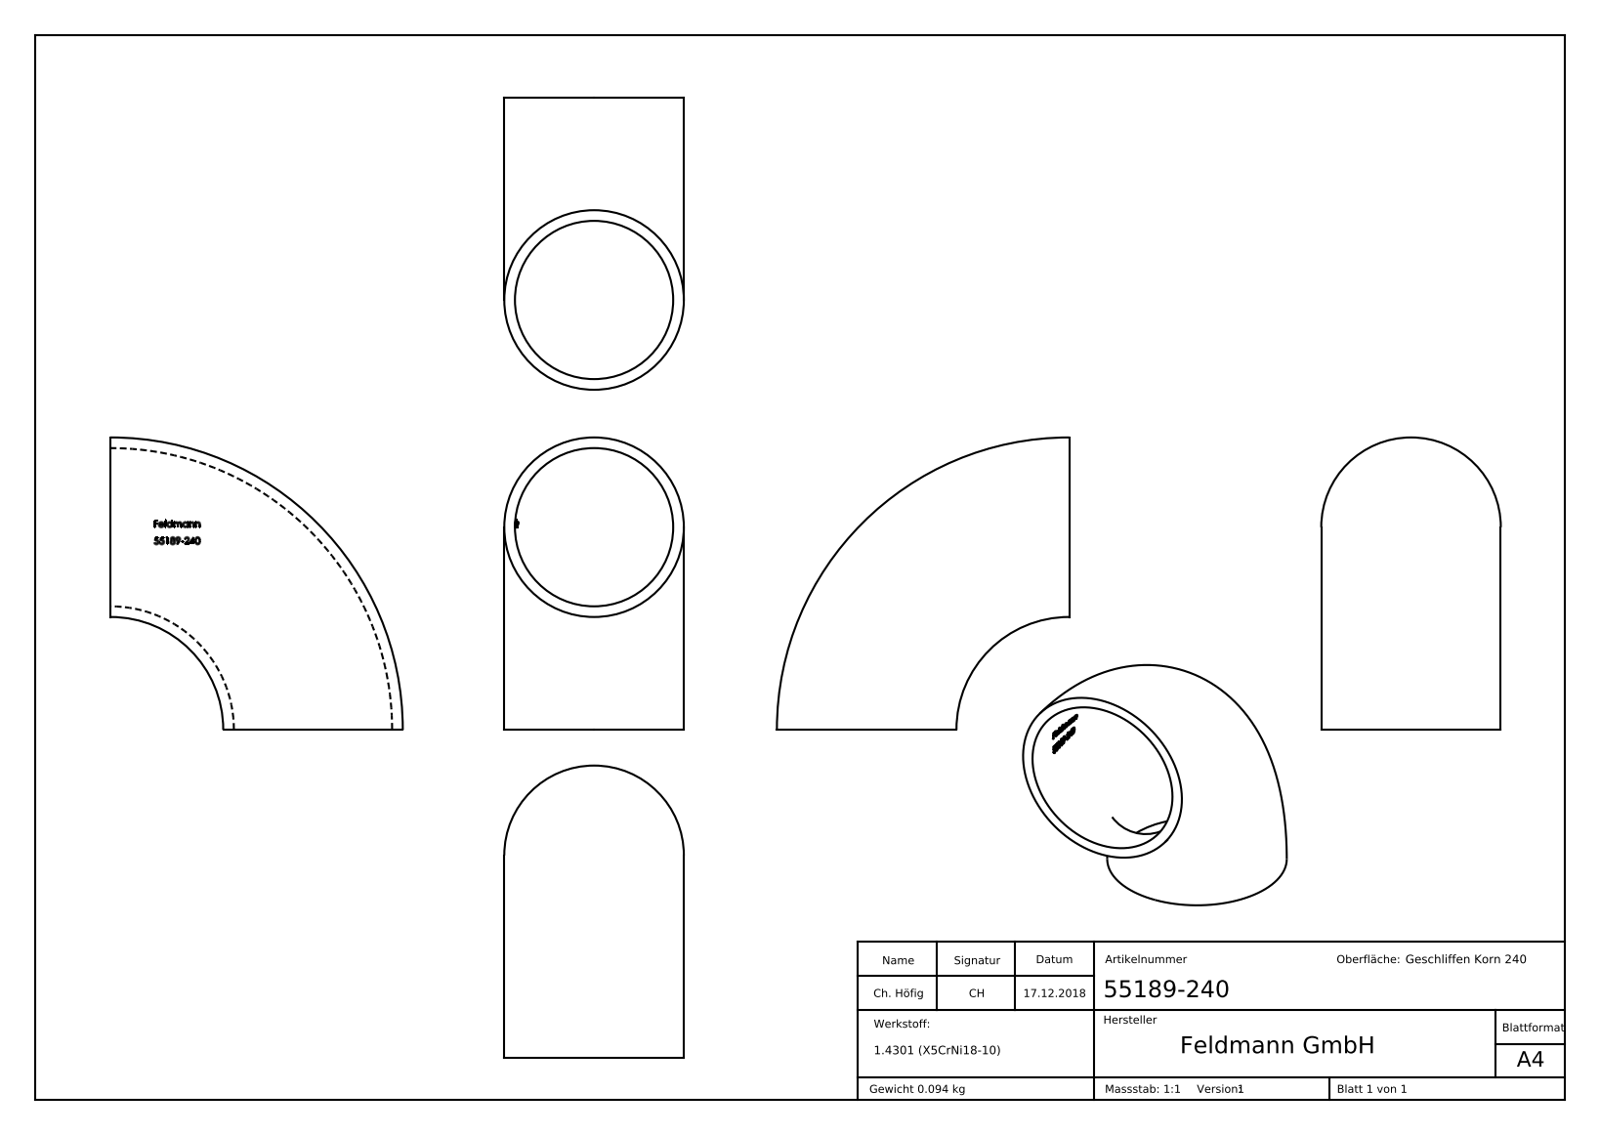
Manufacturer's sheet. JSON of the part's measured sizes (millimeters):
{"part_name": "55189-240", "step_written_by": "SolidWorks 2015 (CONFIG_CONTROL_DESIGN)", "units": "millimeters", "bodies": {"solids": 1, "faces": 234, "planar": 100, "cylindrical": 0, "other": 134}, "overall_size": [54.85, 54.85, 33.7], "volume_mm3": 11888, "surface_area_mm2": 12297, "face_to_face_distances": [0.39, 1.26, 2.97, 1.32, 4.23, 2.02, 3.66, 3.27, 2.4, 0.88]}
